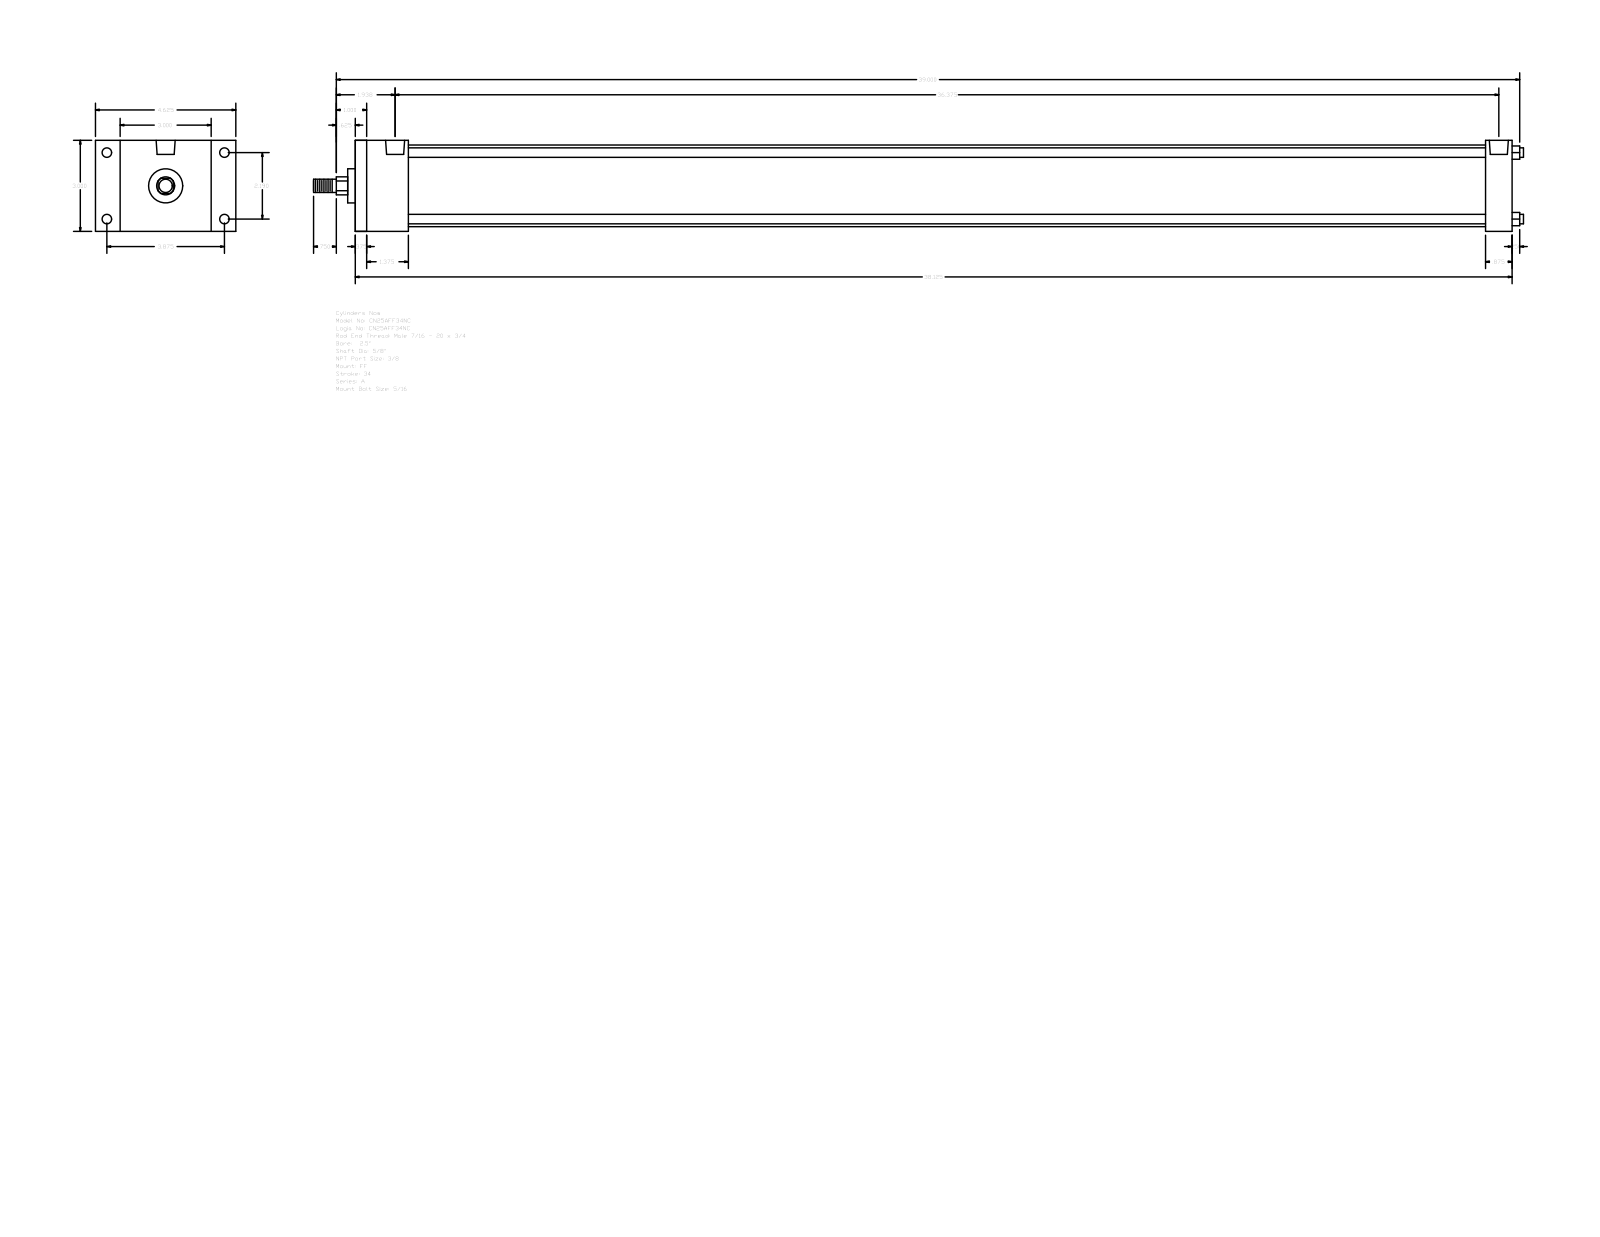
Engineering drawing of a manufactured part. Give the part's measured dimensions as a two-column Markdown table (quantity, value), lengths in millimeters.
| quantity | value |
| --- | --- |
| part name | A_FF__0250_0.625 |
| STEP written by | GSSL Pune (CONFIG_CONTROL_DESIGN) |
| units | millimeters |
| bodies | 0 solids, 92 faces (64 planar, 28 cylindrical, 0 other) |
| overall size | 1012.83 × 117.47 × 76.2 |
| round holes (diameter × count) | 5.56 × 4, 7.94 × 4, 15.93 × 2 |
| round bosses / shafts (diameter × count) | 7.94 × 4, 68.33 × 1, 28.57 × 1, 15.88 × 1, 11.11 × 1 |
| partial cylindrical surfaces (radius × count) | 7.54 × 1 |
| main face-to-face distances | 76.2, 968.37, 9.52, 958.85, 44.45, 34.93, 946.14, 936.62, 901.69, 923.92 |
| hole center spacings | 2.38, 55.62, 98.42, 113.05, 926.31, 928.69, 923.93 |
